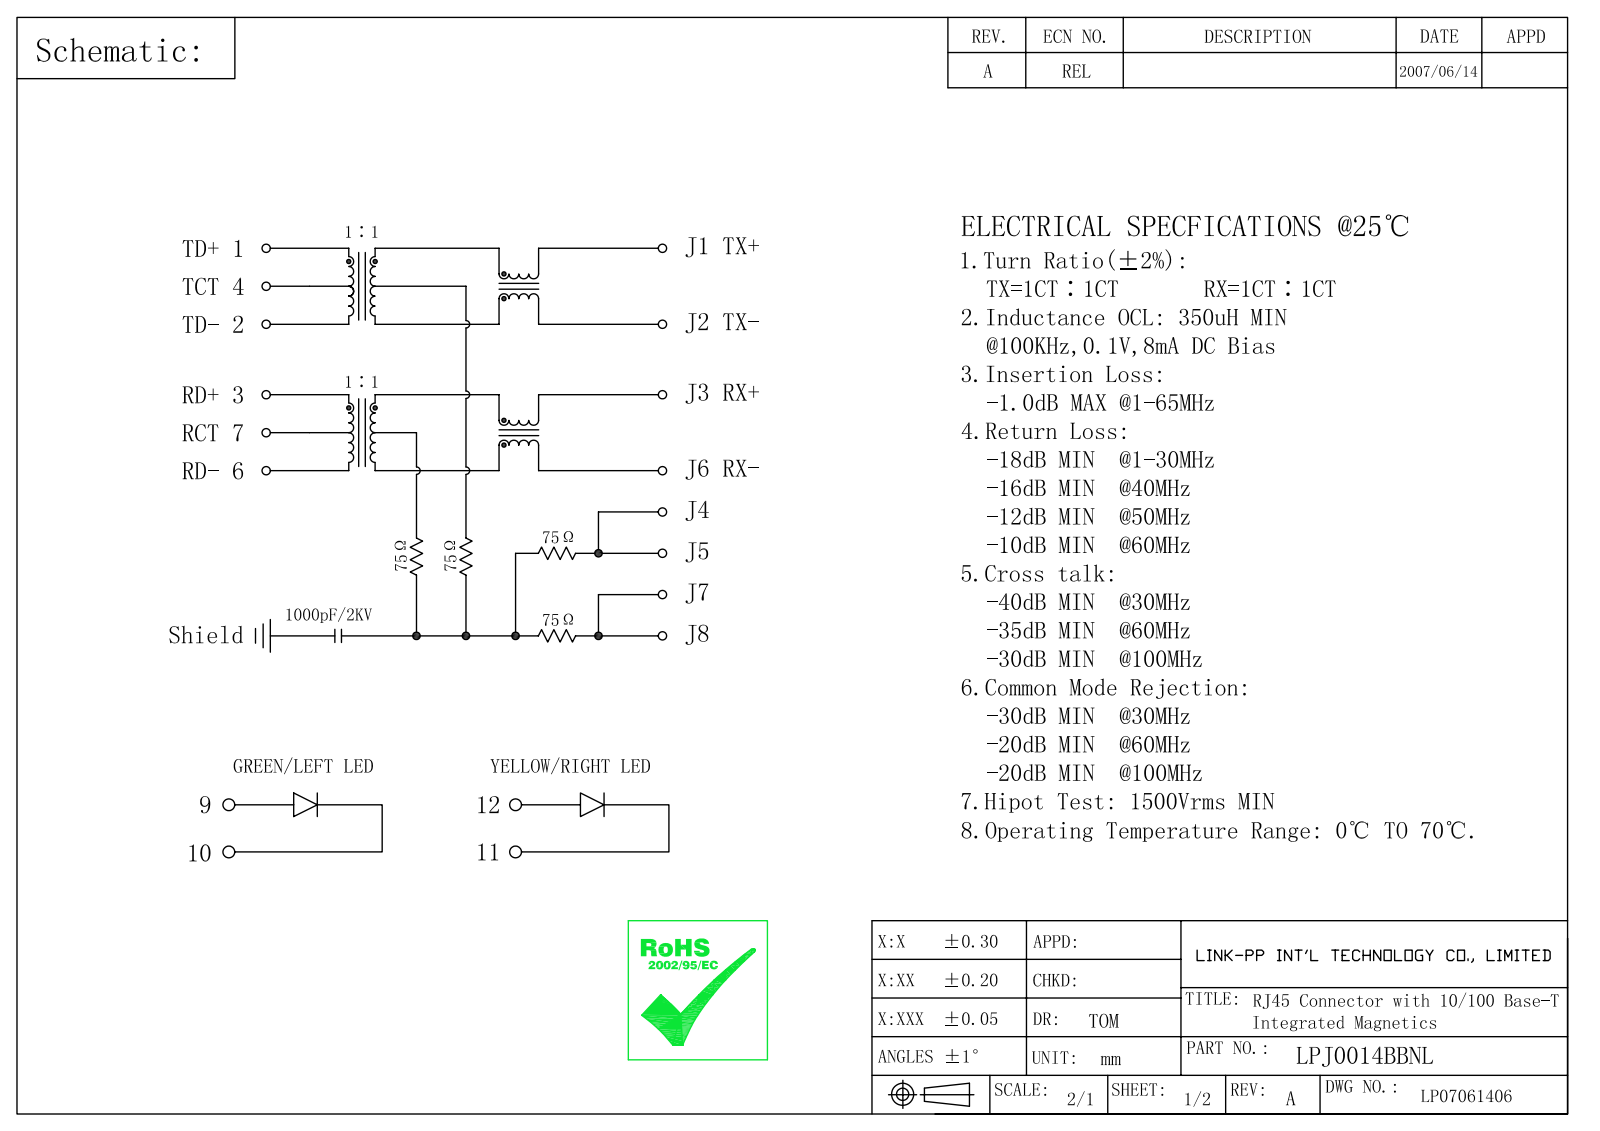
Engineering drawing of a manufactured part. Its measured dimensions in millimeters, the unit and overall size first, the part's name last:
Units: millimetres
Overall size (bounding box): 21.25 × 17.3 × 16.23
Partial cylindrical surfaces — rounded edges, fillets, slot ends (radius × count): R0.1 ×22, R0.15 ×10, R0.2 ×10, R0.23 ×9, R1.21 ×8, R0.5 ×2, R0.6 ×2, R1.57 ×2
Main face-to-face distances: 13.3, 15.93, 2.85, 10.45, 11.45, 9.8, 21.25, 3.65, 9.65, 6.8
Volume: 3 633 mm³ · Surface area: 2 295 mm²
Bodies: 1 solid, 303 faces (178 planar, 81 cylindrical, 44 other)
Part name (STEP PRODUCT): LPJ0013BHNL
STEP written by: SolidWorks 2020 (CONFIG_CONTROL_DESIGN)
